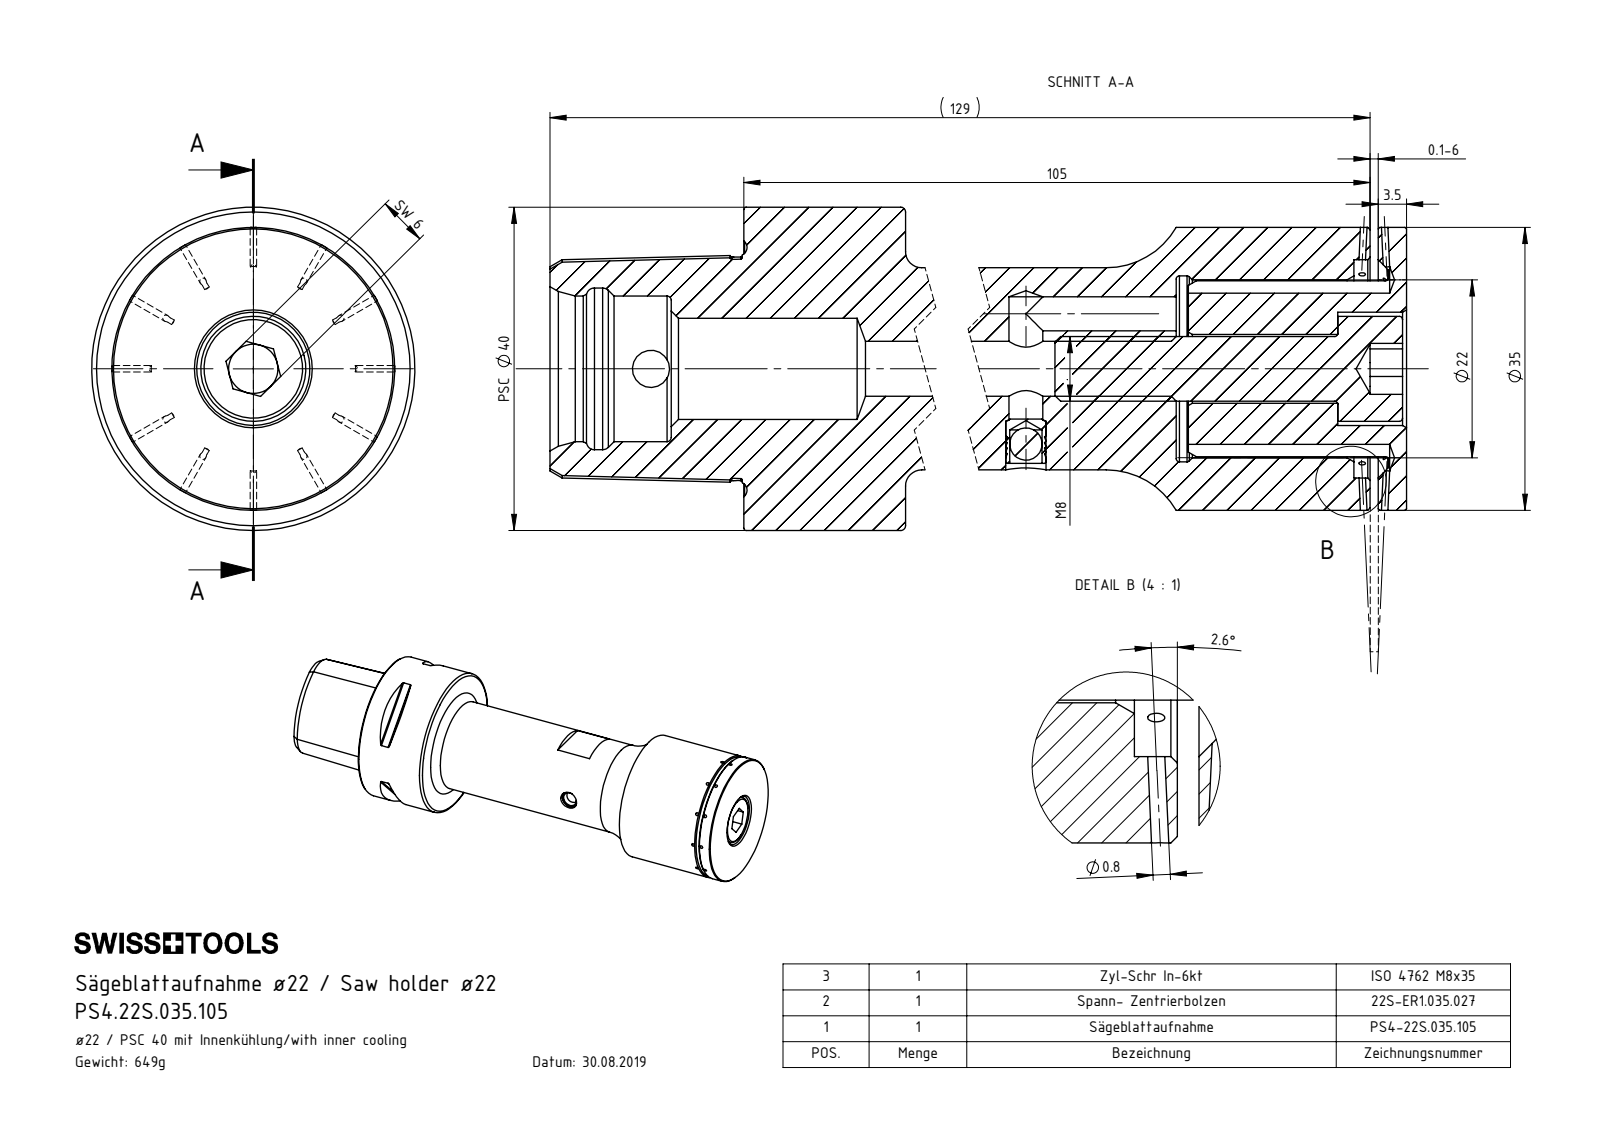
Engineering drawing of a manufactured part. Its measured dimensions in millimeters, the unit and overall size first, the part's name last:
Units: millimetres
Overall size (bounding box): 133.5 × 40 × 40
Round holes (diameter × count): ⌀0.8 ×24, ⌀3.3 ×4, ⌀4 ×2, ⌀4.2 ×2, ⌀4.6 ×1, ⌀6.8 ×1, ⌀8.5 ×1, ⌀12.5 ×1, ⌀14 ×1, ⌀18 ×1, ⌀20 ×1, ⌀23 ×1
Round bosses / shafts (diameter × count): ⌀40 ×1, ⌀35 ×1, ⌀25 ×1, ⌀22 ×1, ⌀13 ×1, ⌀8 ×1, ⌀5 ×1
Partial cylindrical surfaces — rounded edges, fillets, slot ends (radius × count): R0.3 ×8, R3 ×1
Main face-to-face distances: 20, 89.5, 105, 81, 24, 109.5, 106, 86, 3.5, 85
Hole centre spacings: 4.15, 4.14, 11, 15.56, 12.93, 22, 4.2, 6.8
Volume: 84 966 mm³ · Surface area: 27 377 mm²
Bodies: 5 solids, 360 faces (53 planar, 125 cylindrical, 182 other)
Part name (STEP PRODUCT): 22S-ER1.035.027_A; ISO 4762 - M8 x 35; KVT_MB_600_050; PS4.22S.035.105 (+1 more)
STEP written by: SolidWorks 2022 (CONFIG_CONTROL_DESIGN)
